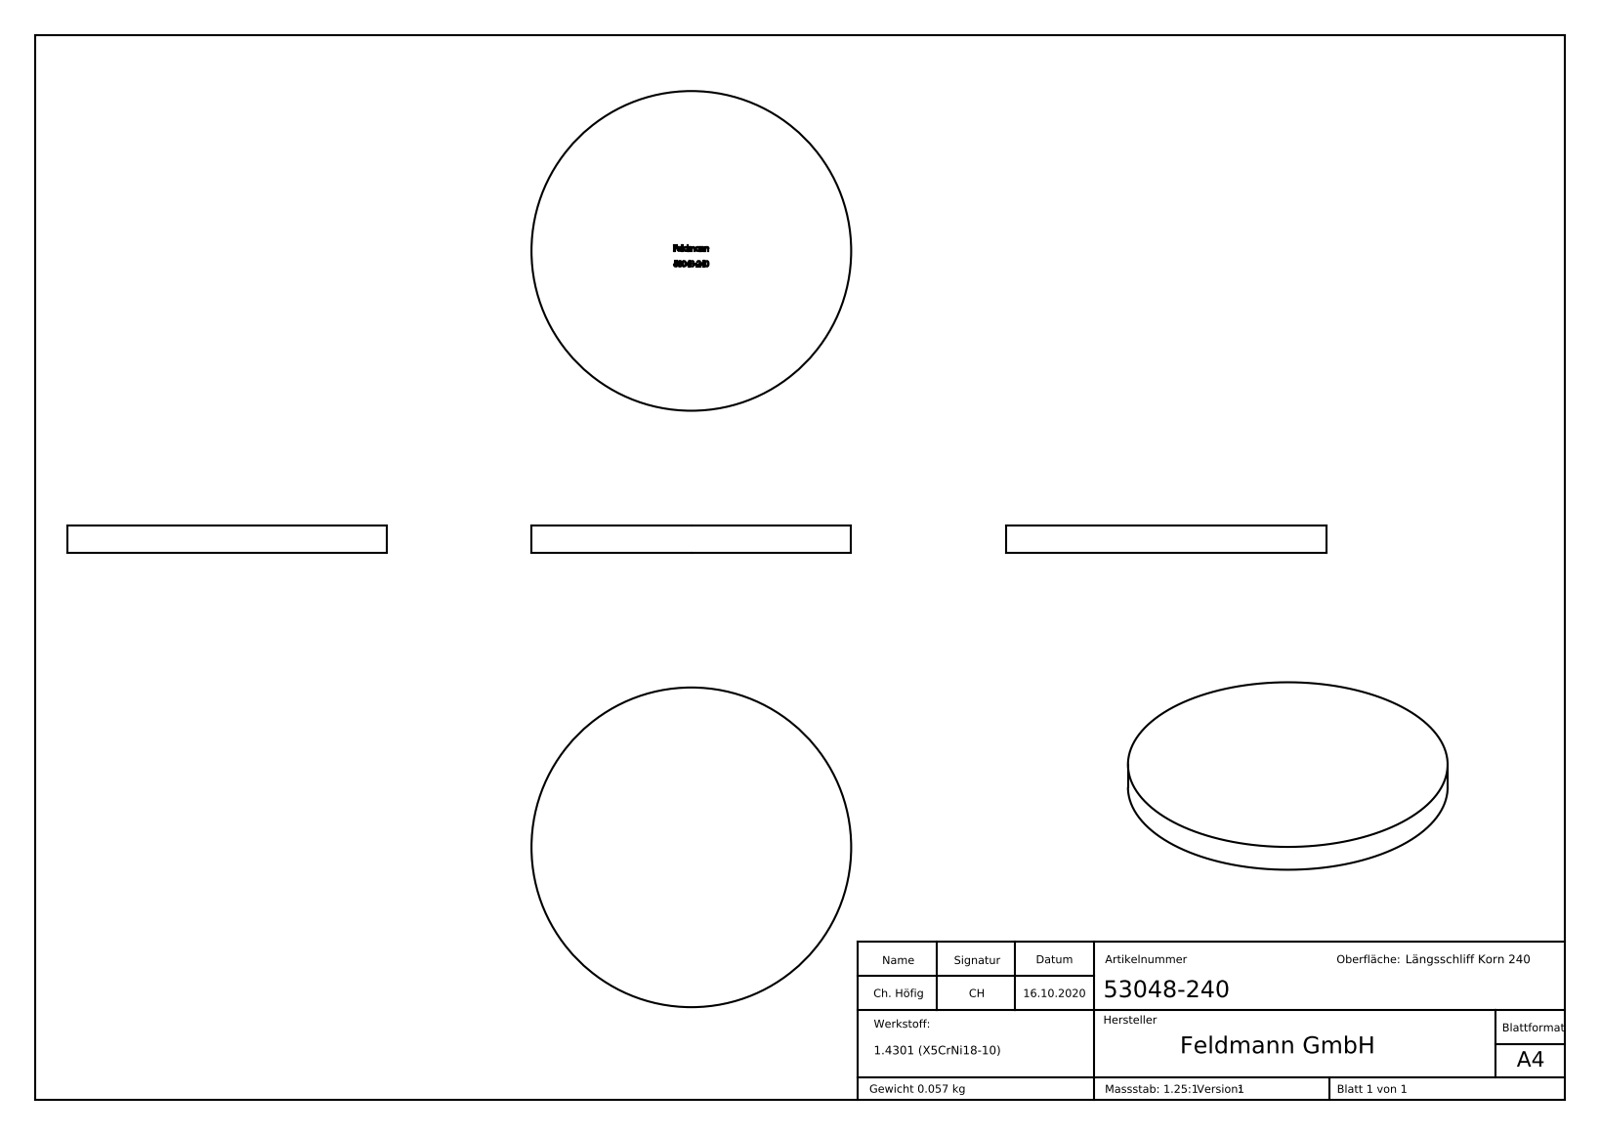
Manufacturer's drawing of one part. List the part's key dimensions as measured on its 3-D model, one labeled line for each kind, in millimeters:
Part name (STEP PRODUCT): 53048-240
STEP written by: SolidWorks 2018 (CONFIG_CONTROL_DESIGN)
Units: millimetres
Bodies: 1 solid, 240 faces (127 planar, 2 cylindrical, 111 other)
Overall size (bounding box): 48 × 48 × 4
Volume: 7 238 mm³ · Surface area: 4 228 mm²
Round bosses / shafts (diameter × count): ⌀48 ×1
Main face-to-face distances: 4, 3.9, 2.2, 1.78, 2.18, 2.45, 0.83, 2.41, 2.25, 0.99
